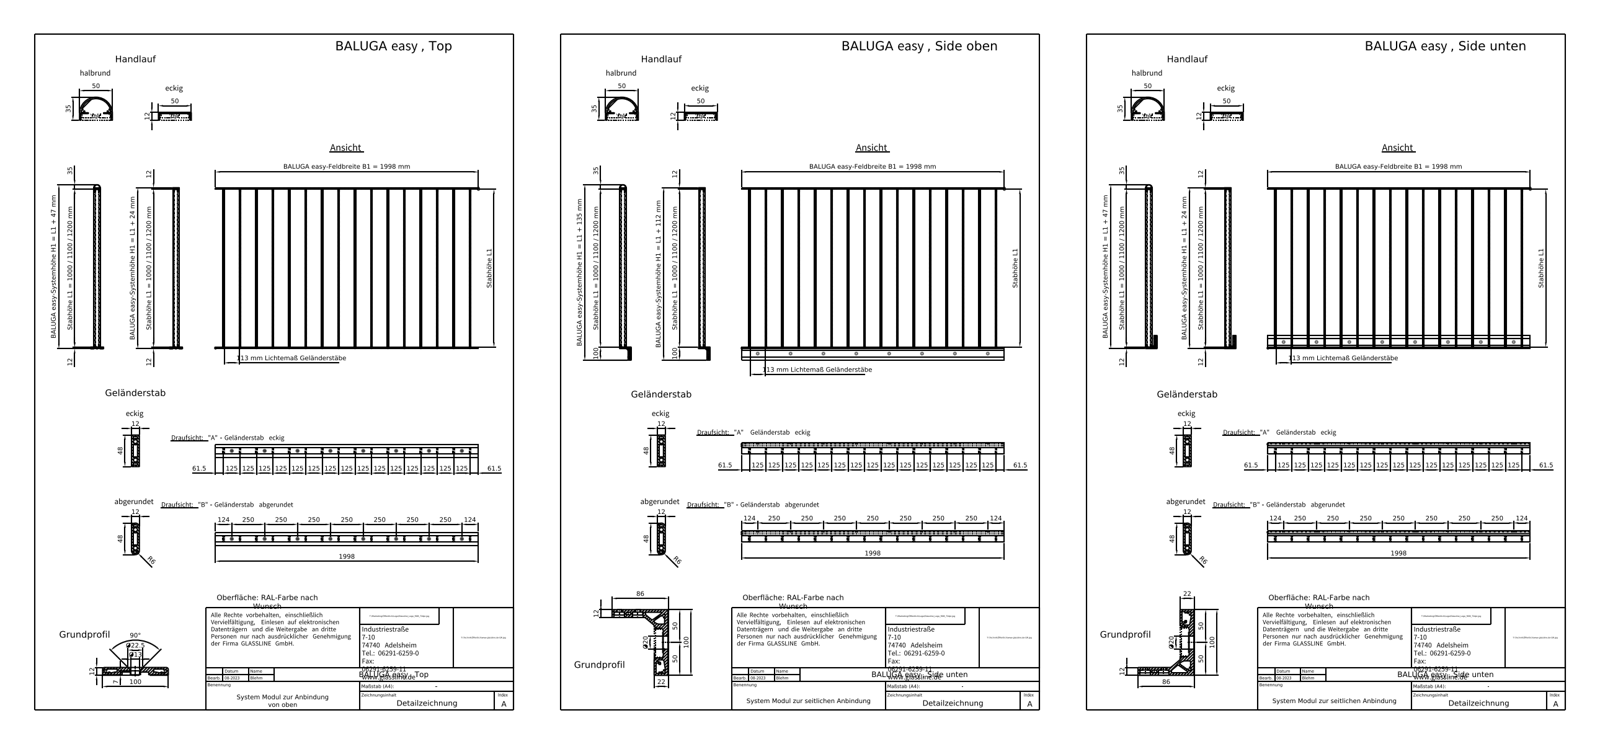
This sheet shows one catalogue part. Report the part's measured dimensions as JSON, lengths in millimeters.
{"part_name": "BALUGA easy_Side oben; Side Up 2000mm; Geländerstab rechteckig 1200mm; Geländerstab abgerundet 1200mm (+3 more)", "step_written_by": "Autodesk Inventor 2024 (AUTOMOTIVE_DESIGN)", "units": "millimeters", "bodies": {"solids": 76, "faces": 11692, "planar": 5392, "cylindrical": 6300, "other": 0}, "overall_size": [3086.01, 1998, 1335], "volume_mm3": 42880000, "surface_area_mm2": 27510000, "round_holes": [[6.5, 128], [16, 128], [20, 8]], "partial_cylinders_radius": [[0.5, 992], [0.3, 532], [0.2, 340], [2, 184], [2.9, 128], [3, 128], [4.85, 128], [1, 88]], "face_to_face_distances": [125, 250, 375, 12, 500, 625, 1000, 137, 113, 262], "hole_center_spacings": [250, 125, 128.1, 500, 251.56, 375, 376.04, 750]}
